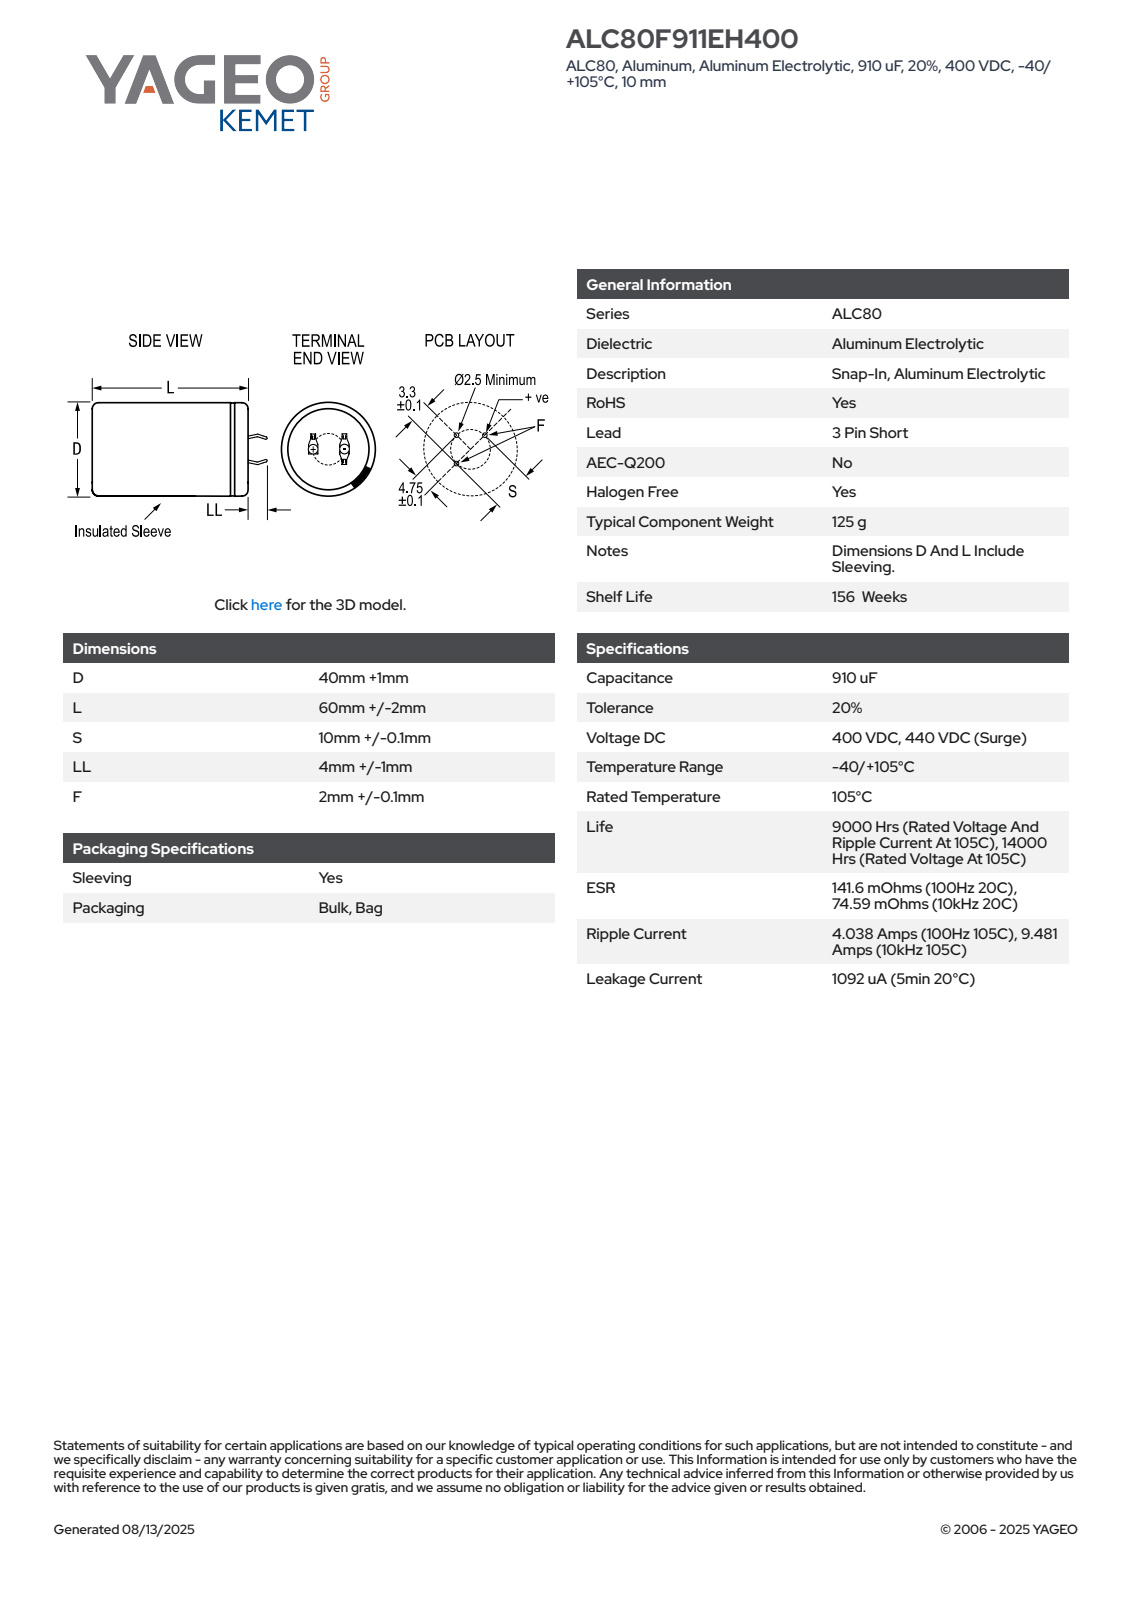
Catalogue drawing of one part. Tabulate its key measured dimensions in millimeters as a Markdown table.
| quantity | value |
| --- | --- |
| part name | CARS_K3P_40X60_D41L62S10LL5F2.1 |
| STEP written by | SolidWorks 2014 (AUTOMOTIVE_DESIGN) |
| units | millimeters |
| bodies | 1 solid, 115 faces (61 planar, 15 cylindrical, 39 other) |
| overall size | 66.99 × 41 × 41 |
| volume | 81 071 mm³ |
| surface area | 10 609 mm² |
| round holes (diameter × count) | 36.28 × 1 |
| round bosses / shafts (diameter × count) | 41 × 1 |
| partial cylindrical surfaces (radius × count) | 20.49 × 1 |
| main face-to-face distances | 61.99, 62.49, 0.5, 0.6, 8.22, 0.75, 1.35, 0.59, 0.58, 7.47 |
